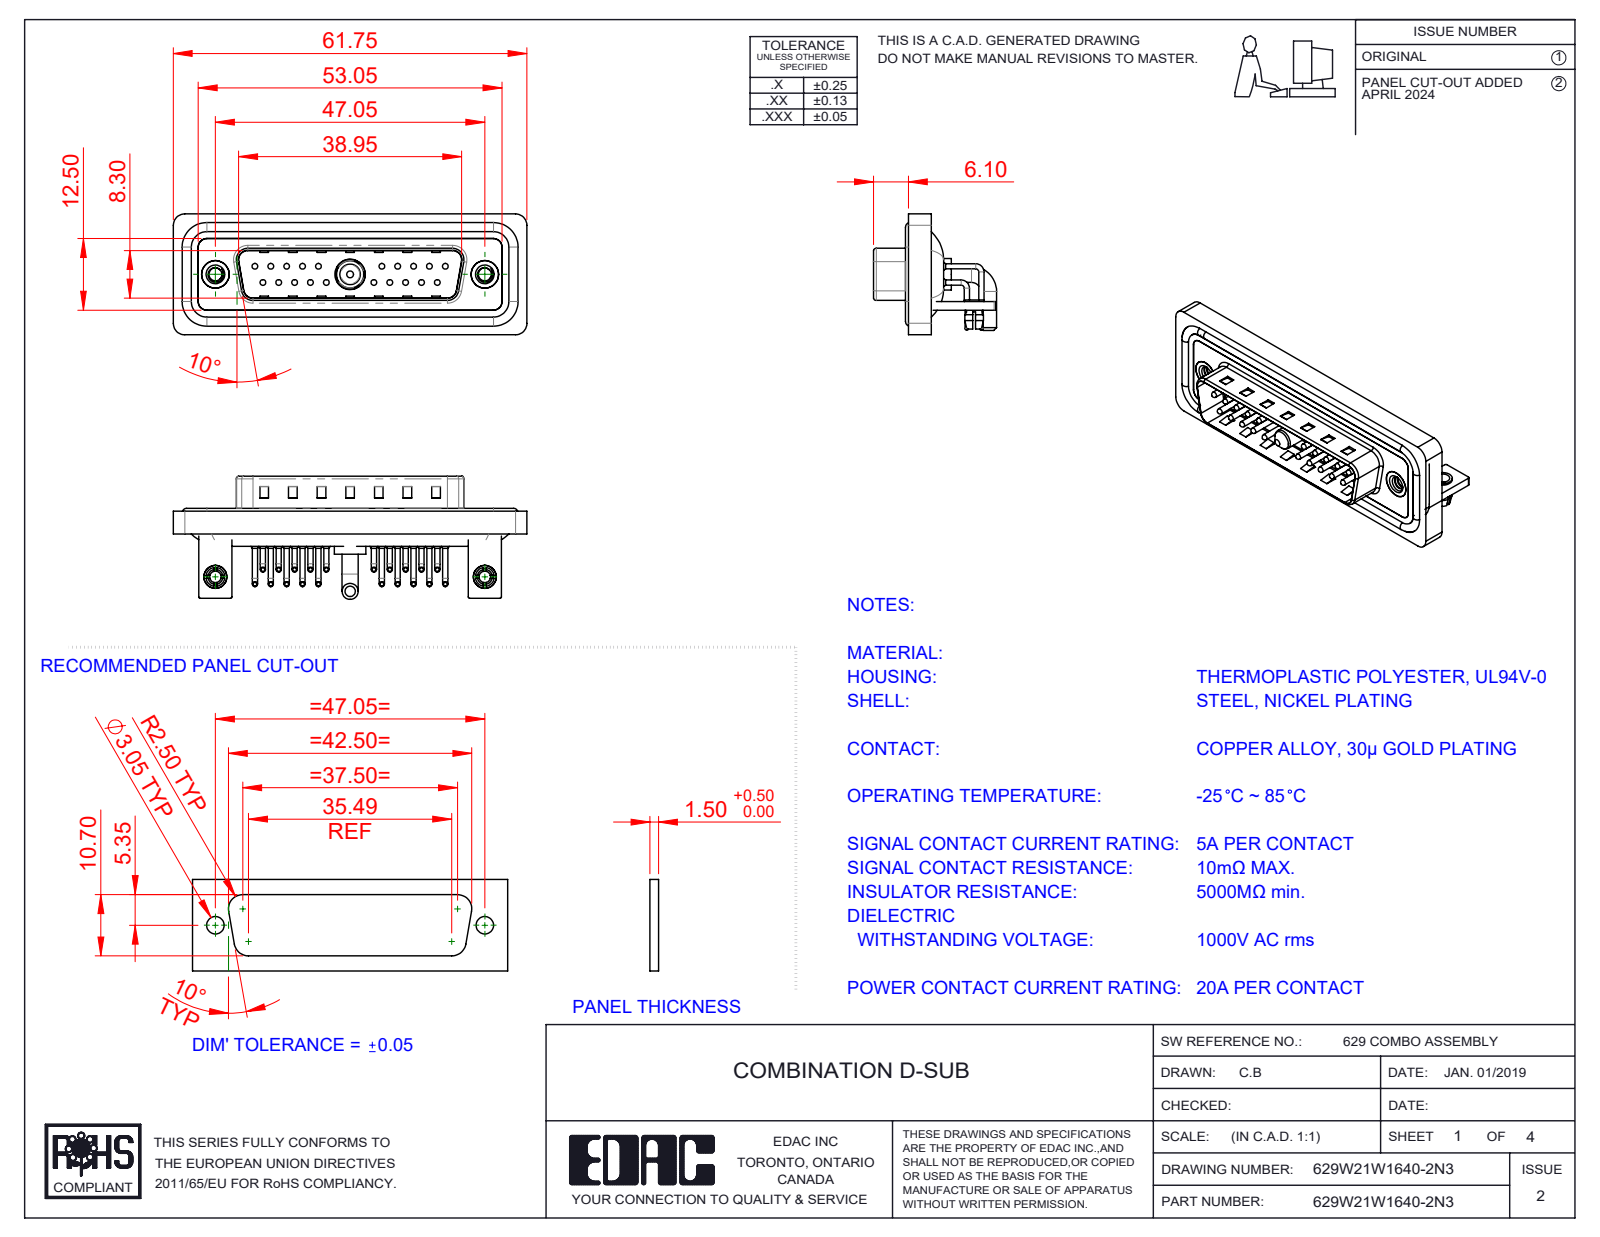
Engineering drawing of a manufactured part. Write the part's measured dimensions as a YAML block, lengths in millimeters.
part_name: "629Combo Contact Row 2; 629Combo Board Lock; 629W21W1640-2N3; 629Combo Waterproof Housing_25 Contacts (+7 more)"
step_written_by: "SolidWorks 2023 (CONFIG_CONTROL_DESIGN)"
units: millimeters
bodies: {solids: 33, faces: 2858, planar: 1567, cylindrical: 979, other: 312}
overall_size: [61.75, 21.5, 21.1]
volume: 7732
surface_area: 13518
round_holes:
  - {diameter: 2, count: 22}
  - {diameter: 0.75, count: 20}
  - {diameter: 1.6, count: 20}
  - {diameter: 2.26, count: 2}
  - {diameter: 2.5, count: 2}
  - {diameter: 3.2, count: 2}
  - {diameter: 4, count: 2}
  - {diameter: 4.8, count: 2}
  - {diameter: 5, count: 2}
  - {diameter: 4.85, count: 1}
  - {diameter: 5.3, count: 1}
round_bosses_or_shafts:
  - {diameter: 0.9, count: 40}
  - {diameter: 1.5, count: 20}
  - {diameter: 1, count: 20}
  - {diameter: 0.65, count: 20}
  - {diameter: 1.6, count: 4}
  - {diameter: 4.9, count: 2}
  - {diameter: 4, count: 2}
  - {diameter: 3.4, count: 2}
partial_cylinders:
  - {radius: 1.01, count: 20}
  - {radius: 2, count: 19}
  - {radius: 1.5, count: 18}
  - {radius: 0.25, count: 16}
  - {radius: 0.5, count: 9}
  - {radius: 1.6, count: 8}
  - {radius: 0.6, count: 4}
  - {radius: 0.65, count: 4}
face_to_face_distances: [0.4, 0.8, 2.1, 2.9, 1.5, 1.1, 4.1, 1.6, 4.5, 3.7]
hole_center_spacings: [3.16, 2.77, 5.54, 8.31, 5.04, 19.39, 20.97, 22.16]
